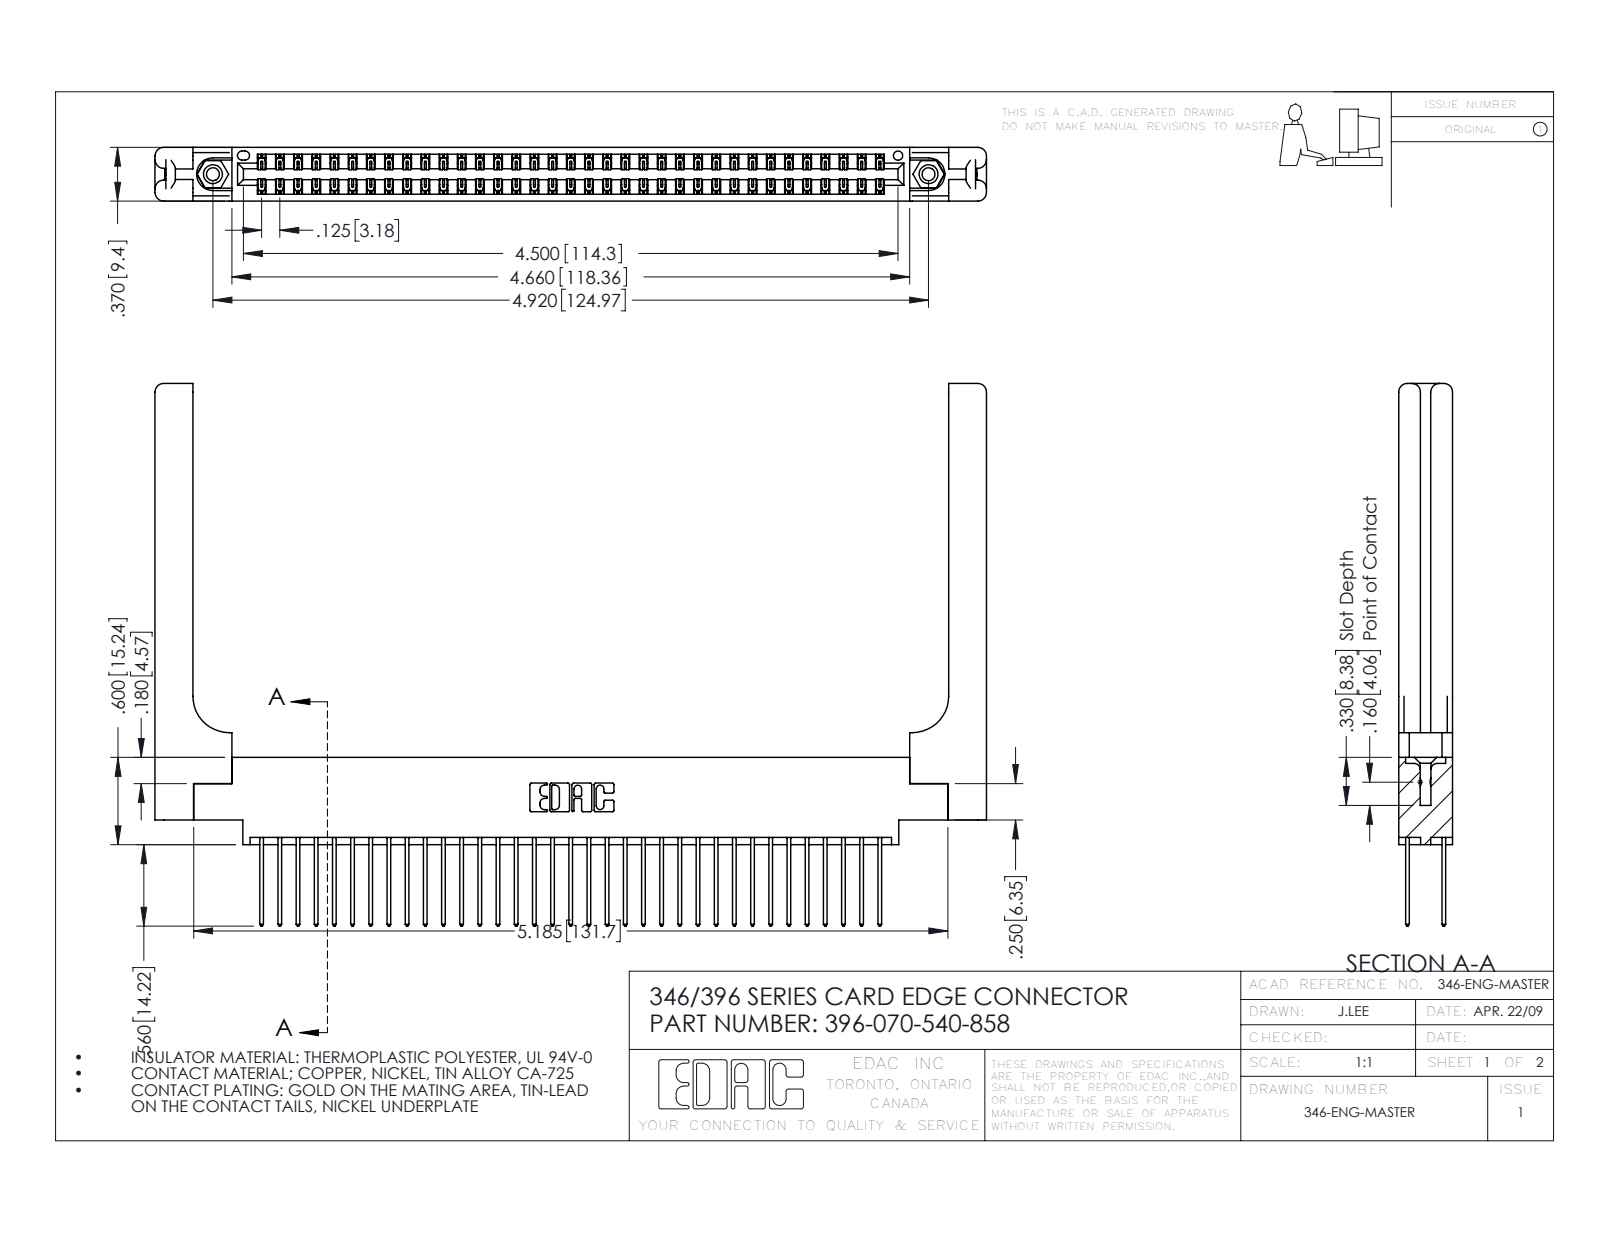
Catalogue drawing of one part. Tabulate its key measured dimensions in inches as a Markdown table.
| quantity | value |
| --- | --- |
| part name | 345-250-001_345-250-001-102; 396-070-540-858; 345-292-001_345-293-140; 346 Part_0.170 Offset - 0.156 Dia-TH (+1 more) |
| STEP written by | SolidWorks 2016 (CONFIG_CONTROL_DESIGN) |
| units | inches |
| bodies | 75 solids, 4022 faces (2678 planar, 1284 cylindrical, 60 other) |
| overall size | 5.716 × 3.73 × 0.37 |
| volume | 1.325 in³ |
| surface area | 40.05 in² |
| round holes (diameter × count) | 0.089 × 2, 0.125 × 2, 0.156 × 2, 0.064 × 1 |
| round bosses / shafts (diameter × count) | 0.155 × 2 |
| partial cylindrical surfaces (radius × count) | 0.006 × 105, 0.01 × 70, 0.01 × 22, 0.06 × 16, 0.007 × 6, 0.031 × 6, 0.026 × 3, 0.014 × 2 |
| main face-to-face distances | 0.048, 0.322, 0.37, 0.072, 0.25, 0.025, 0.298, 0.148, 0.15, 0.275 |
| hole center spacings | 0.246, 4.711, 4.92 |
